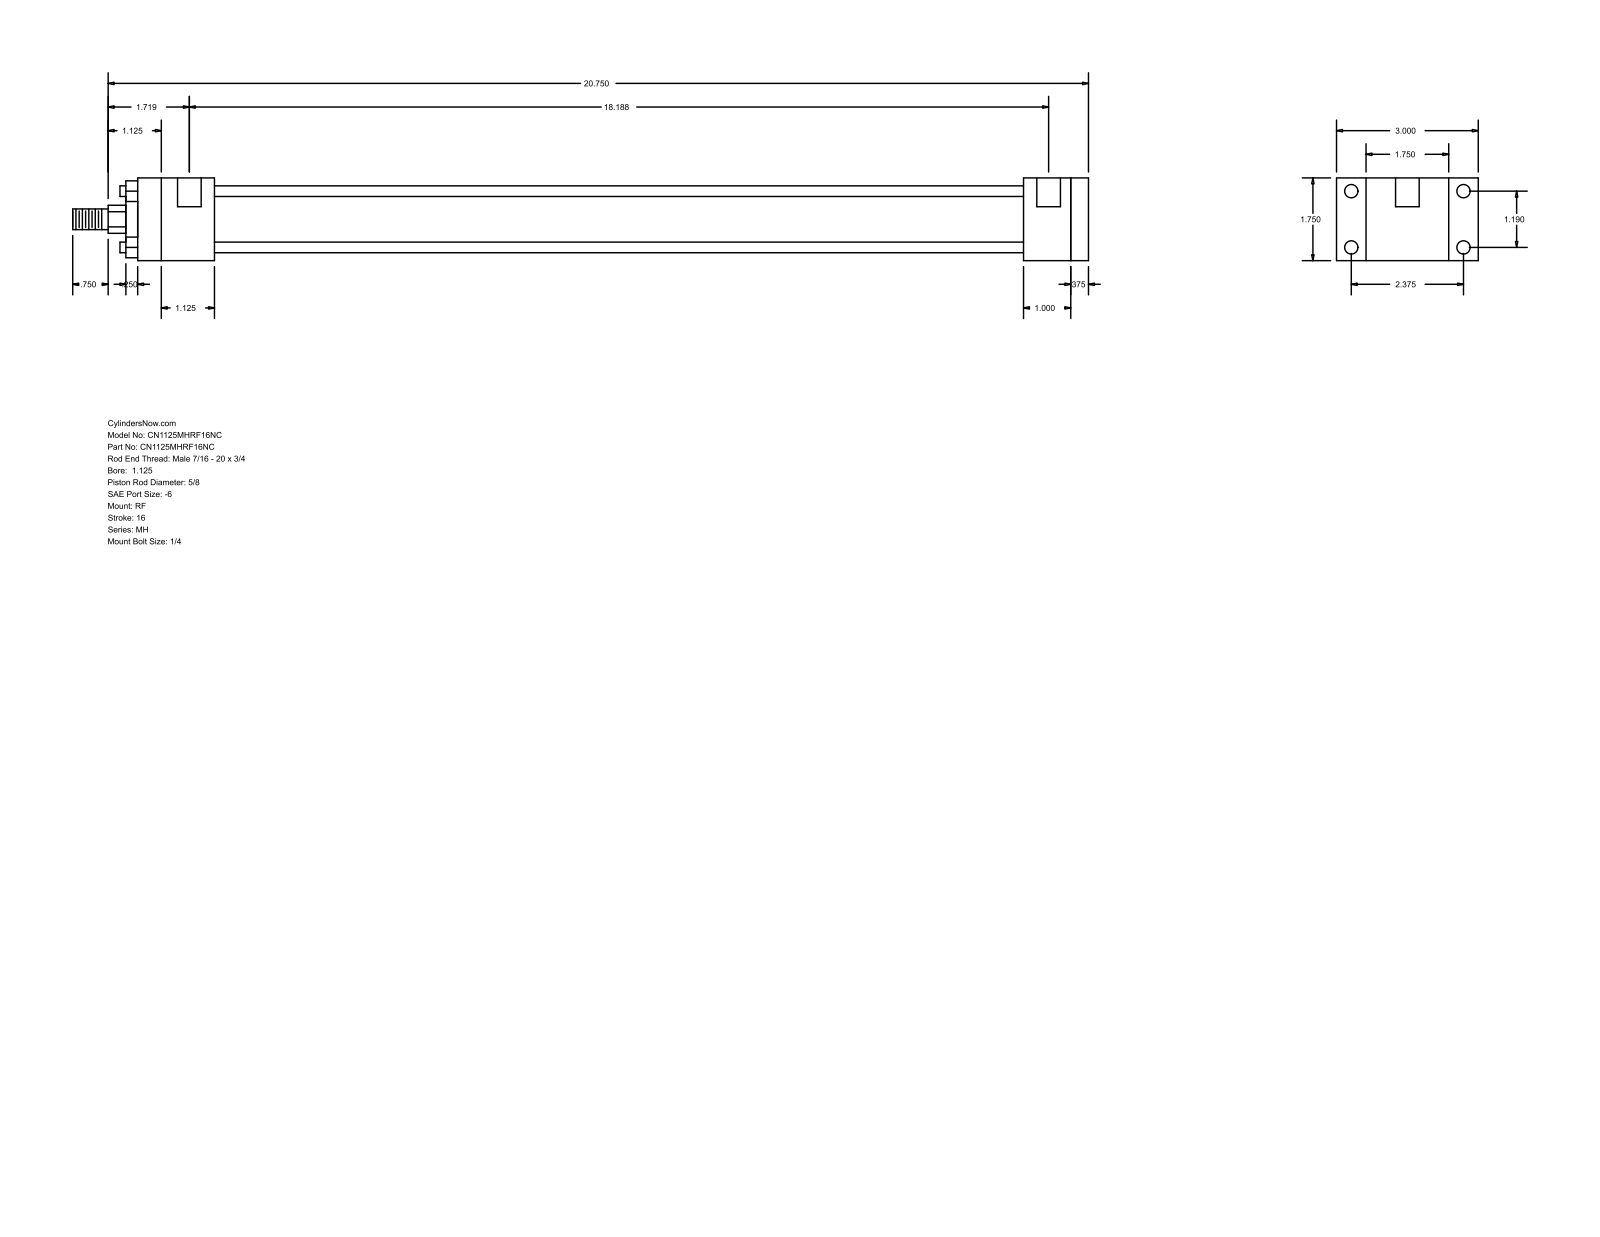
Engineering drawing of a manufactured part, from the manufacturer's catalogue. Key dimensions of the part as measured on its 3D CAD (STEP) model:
Part name (STEP PRODUCT): MH_RF__0112_0.625
STEP written by: GSSL Pune (CONFIG_CONTROL_DESIGN)
Units: millimetres
Bodies: 0 solids, 92 faces (64 planar, 28 cylindrical, 0 other)
Overall size (bounding box): 546.1 × 76.2 × 44.45
Round holes (diameter × count): ⌀5.56 ×4, ⌀7.14 ×4, ⌀12.7 ×2
Round bosses / shafts (diameter × count): ⌀5.71 ×4, ⌀34.92 ×1, ⌀28.57 ×1, ⌀15.88 ×1, ⌀11.11 ×1
Partial cylindrical surfaces — rounded edges, fillets, slot ends (radius × count): R7.54 ×1
Main face-to-face distances: 44.46, 9.53, 511.17, 25.4, 34.93, 15.87, 460.37, 469.9, 434.97, 41.27
Hole centre spacings: 30.22, 60.32, 67.47, 458.79, 3.17, 461.96
